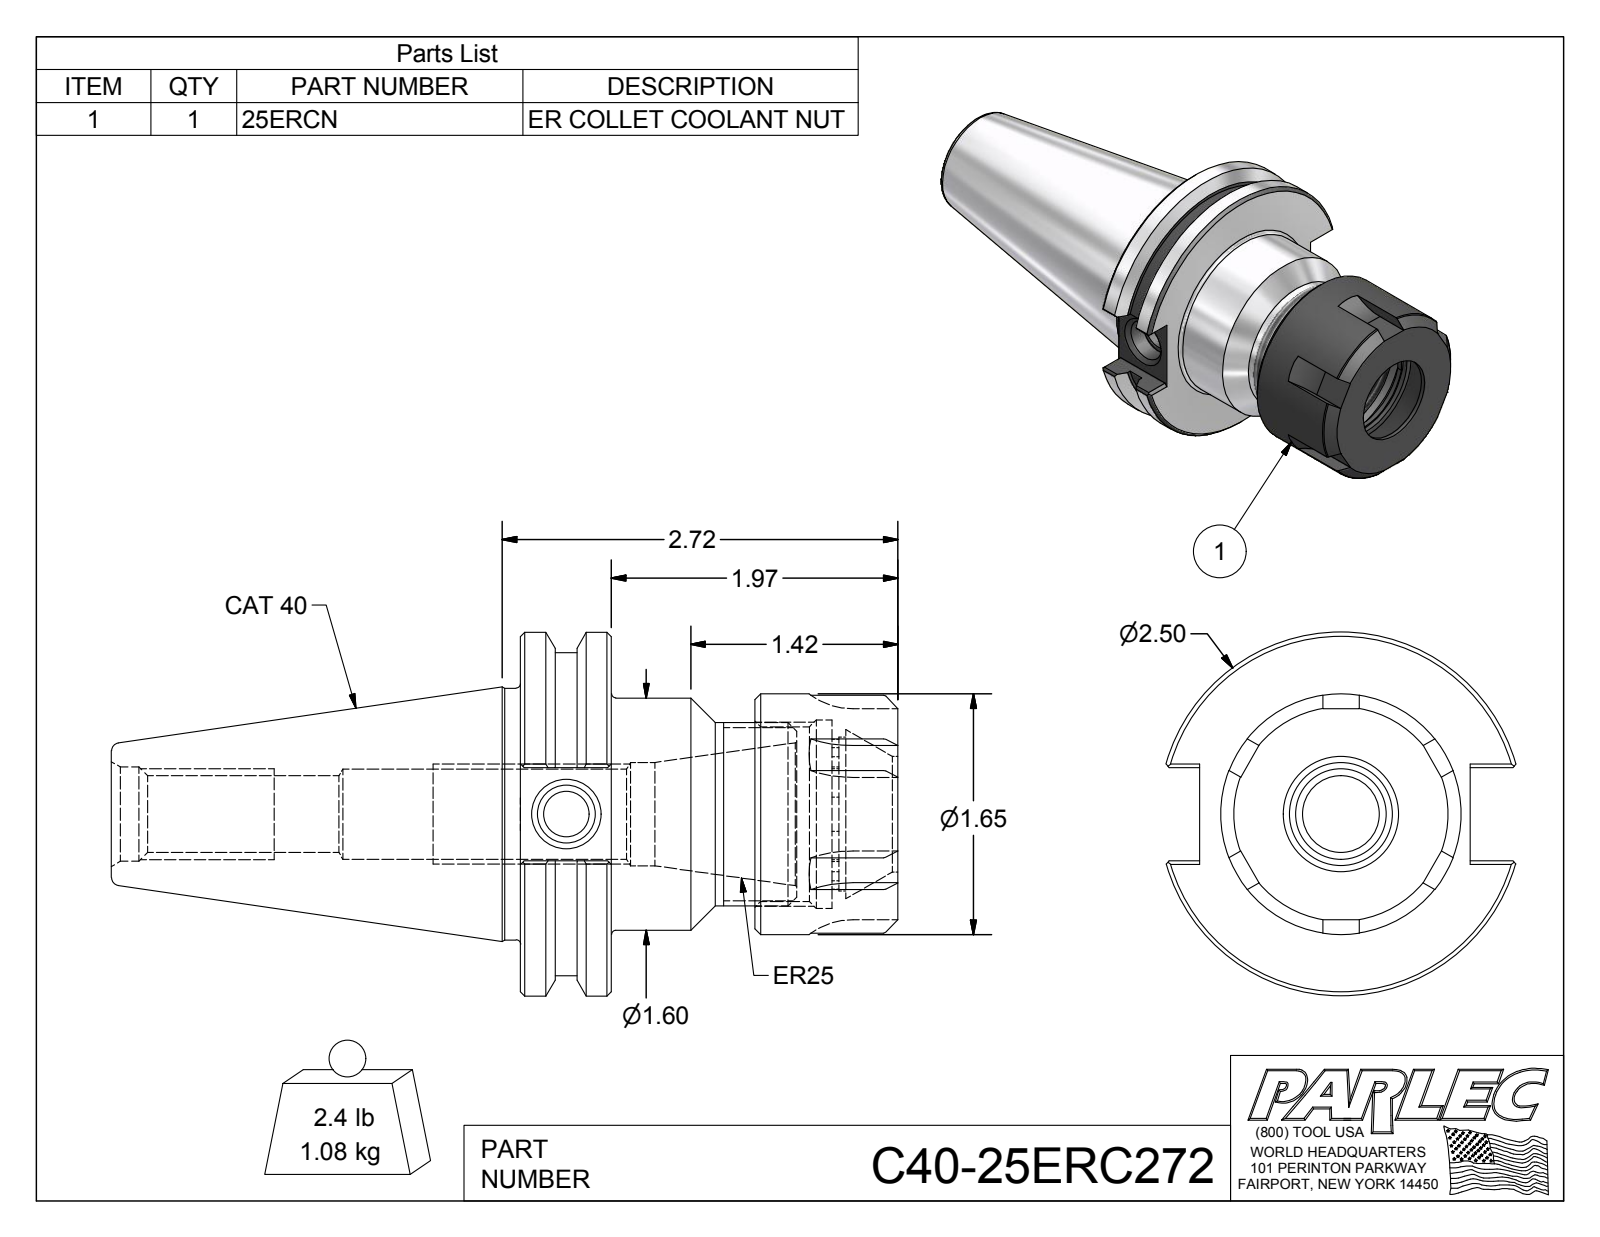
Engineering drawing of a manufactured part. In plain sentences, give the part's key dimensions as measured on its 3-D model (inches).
The part is named "C40-25ER2-1; 25ERCN; C40-25ERC272". Its 3-D file was written by "Autodesk Inventor 2016 (AUTOMOTIVE_DESIGN)". It is 2 solids with 129 faces: 59 planar, 31 cylindrical and 39 other. Overall it measures 5.407 by 2.5 by 2.404 inches. Its volume is 8.407 cubic inches and its surface area 51.88 square inches. Round holes: 1 of diameter 0.315, 1 of diameter 0.396, 1 of diameter 0.527, 1 of diameter 0.62, 1 of diameter 0.648, 1 of diameter 0.71, 1 of diameter 0.794, 1 of diameter 1.057, 1 of diameter 1.201, 1 of diameter 1.294. Round bosses or shafts: 1 of diameter 2.5, 1 of diameter 2.219, 1 of diameter 1.73, 1 of diameter 1.654, 1 of diameter 1.595, 1 of diameter 1.26. Partial cylindrical surfaces (rounded edges, fillets, slot ends): 6 of radius 0.5, 1 of radius 0.472, 1 of radius 0.515. The main face-to-face distances are 0.625, 2.595, 1.97, 1.611, 0.986, 0.984, 2.143, 1.517, 0.531, 0.453.
